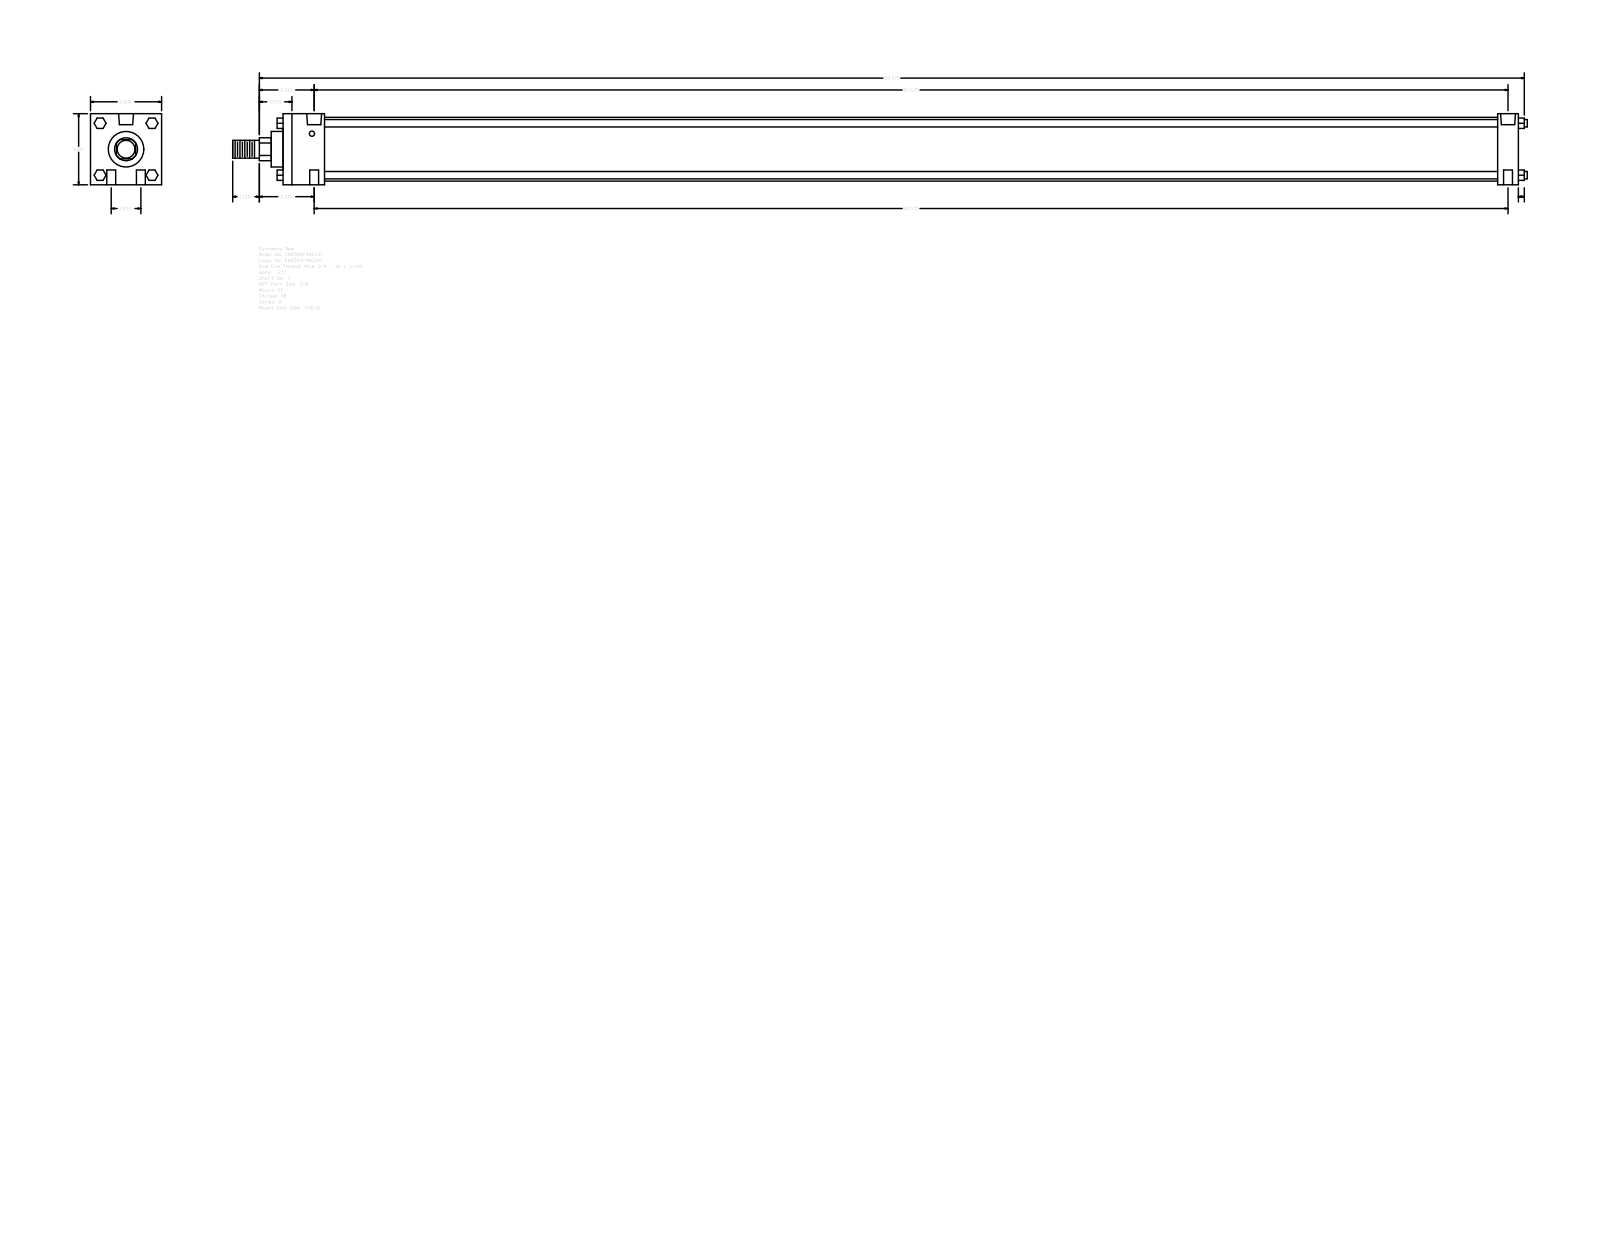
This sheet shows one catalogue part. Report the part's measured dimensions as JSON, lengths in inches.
{"part_name": "A_SF__0250_1", "step_written_by": "GSSL Pune (CONFIG_CONTROL_DESIGN)", "units": "inches", "bodies": {"solids": 0, "faces": 124, "planar": 94, "cylindrical": 30, "other": 0}, "overall_size": [54.625, 3, 3], "round_holes": [[0.375, 4], [0.219, 2], [0.627, 2]], "round_bosses_or_shafts": [[0.313, 4], [2.69, 1], [1.5, 1], [1, 1], [0.75, 1]], "partial_cylinders_radius": [[0.484, 1]], "face_to_face_distances": [3, 52.125, 51.25, 0.875, 1.75, 49.5, 50.375, 0.5, 0.437, 2.25], "hole_center_spacings": [0.625, 50.379, 50.375, 1.25, 50.39, 50.562]}
